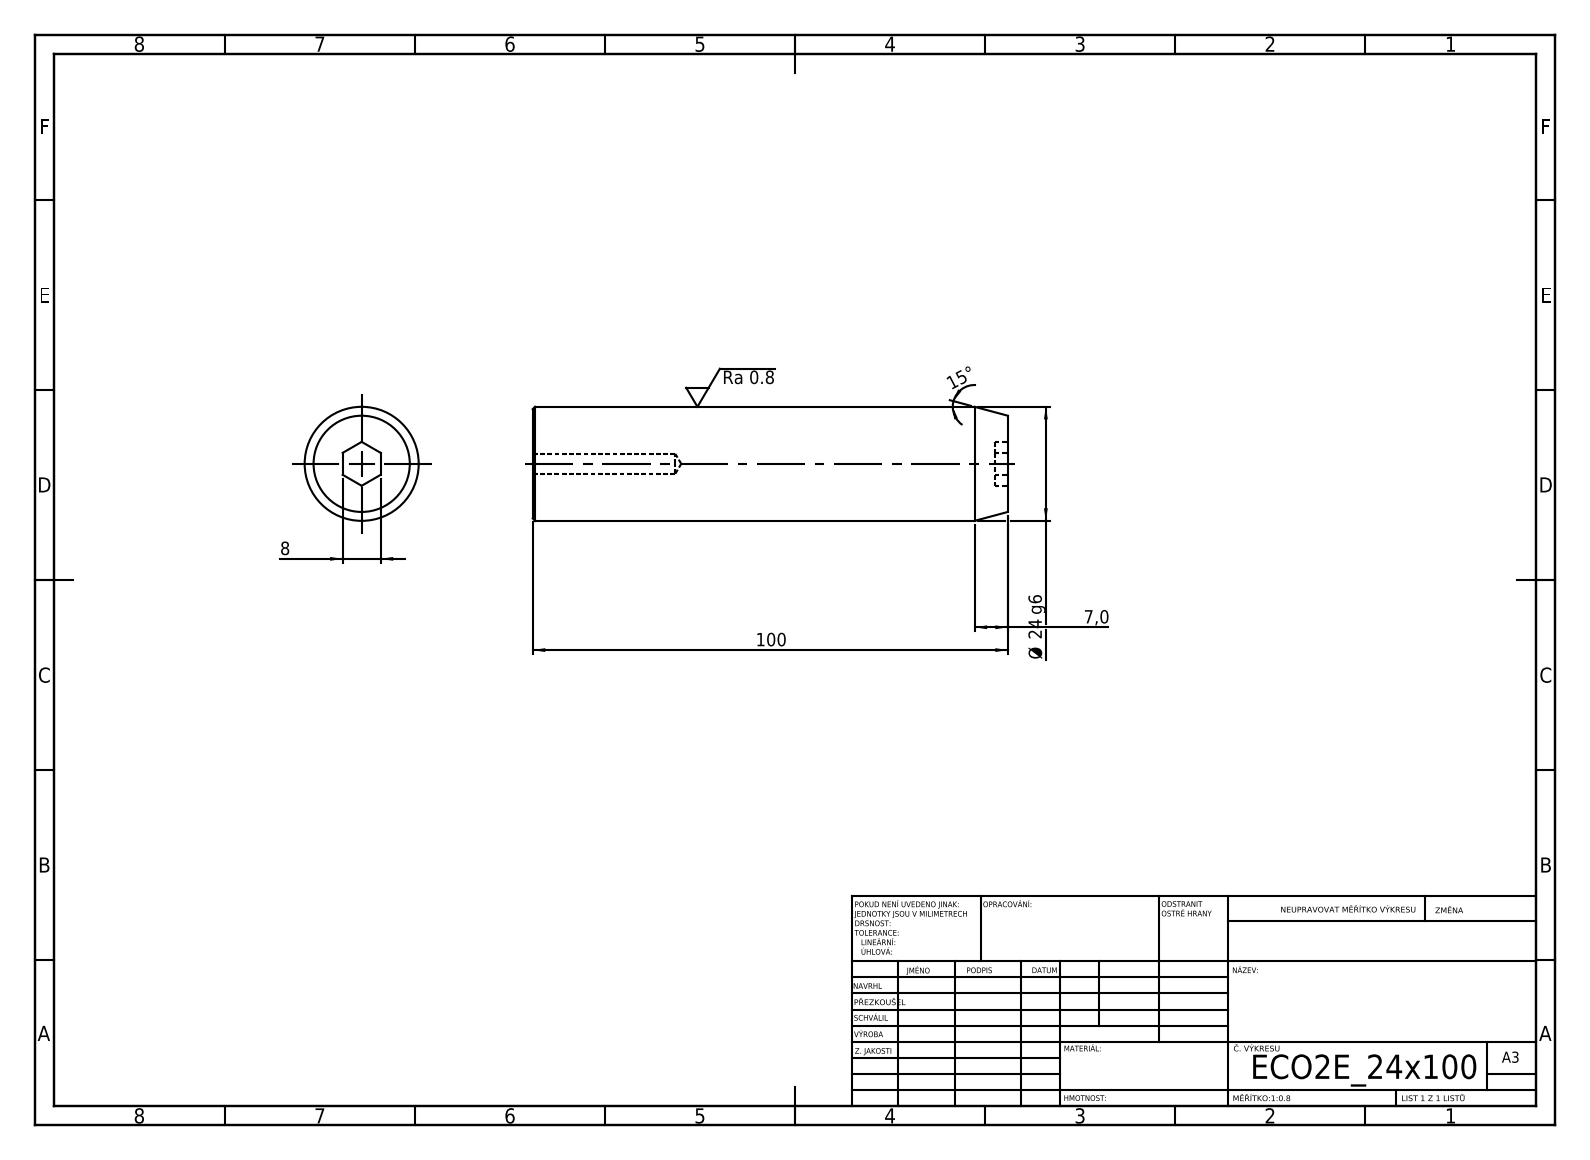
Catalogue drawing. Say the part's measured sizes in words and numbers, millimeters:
Its 3-D file was written by "SolidWorks 2019 (CONFIG_CONTROL_DESIGN)". It is 1 solid with 19 faces: 9 planar, 4 cylindrical and 6 other. Overall it measures 100 by 24 by 24 millimeters. Its volume is 44 184 cubic millimeters and its surface area 8 743 square millimeters. Round holes: 1 of diameter 4.2. Round bosses or shafts: 1 of diameter 24. The main face-to-face distances are 100, 2.8, 97.2, 8.
